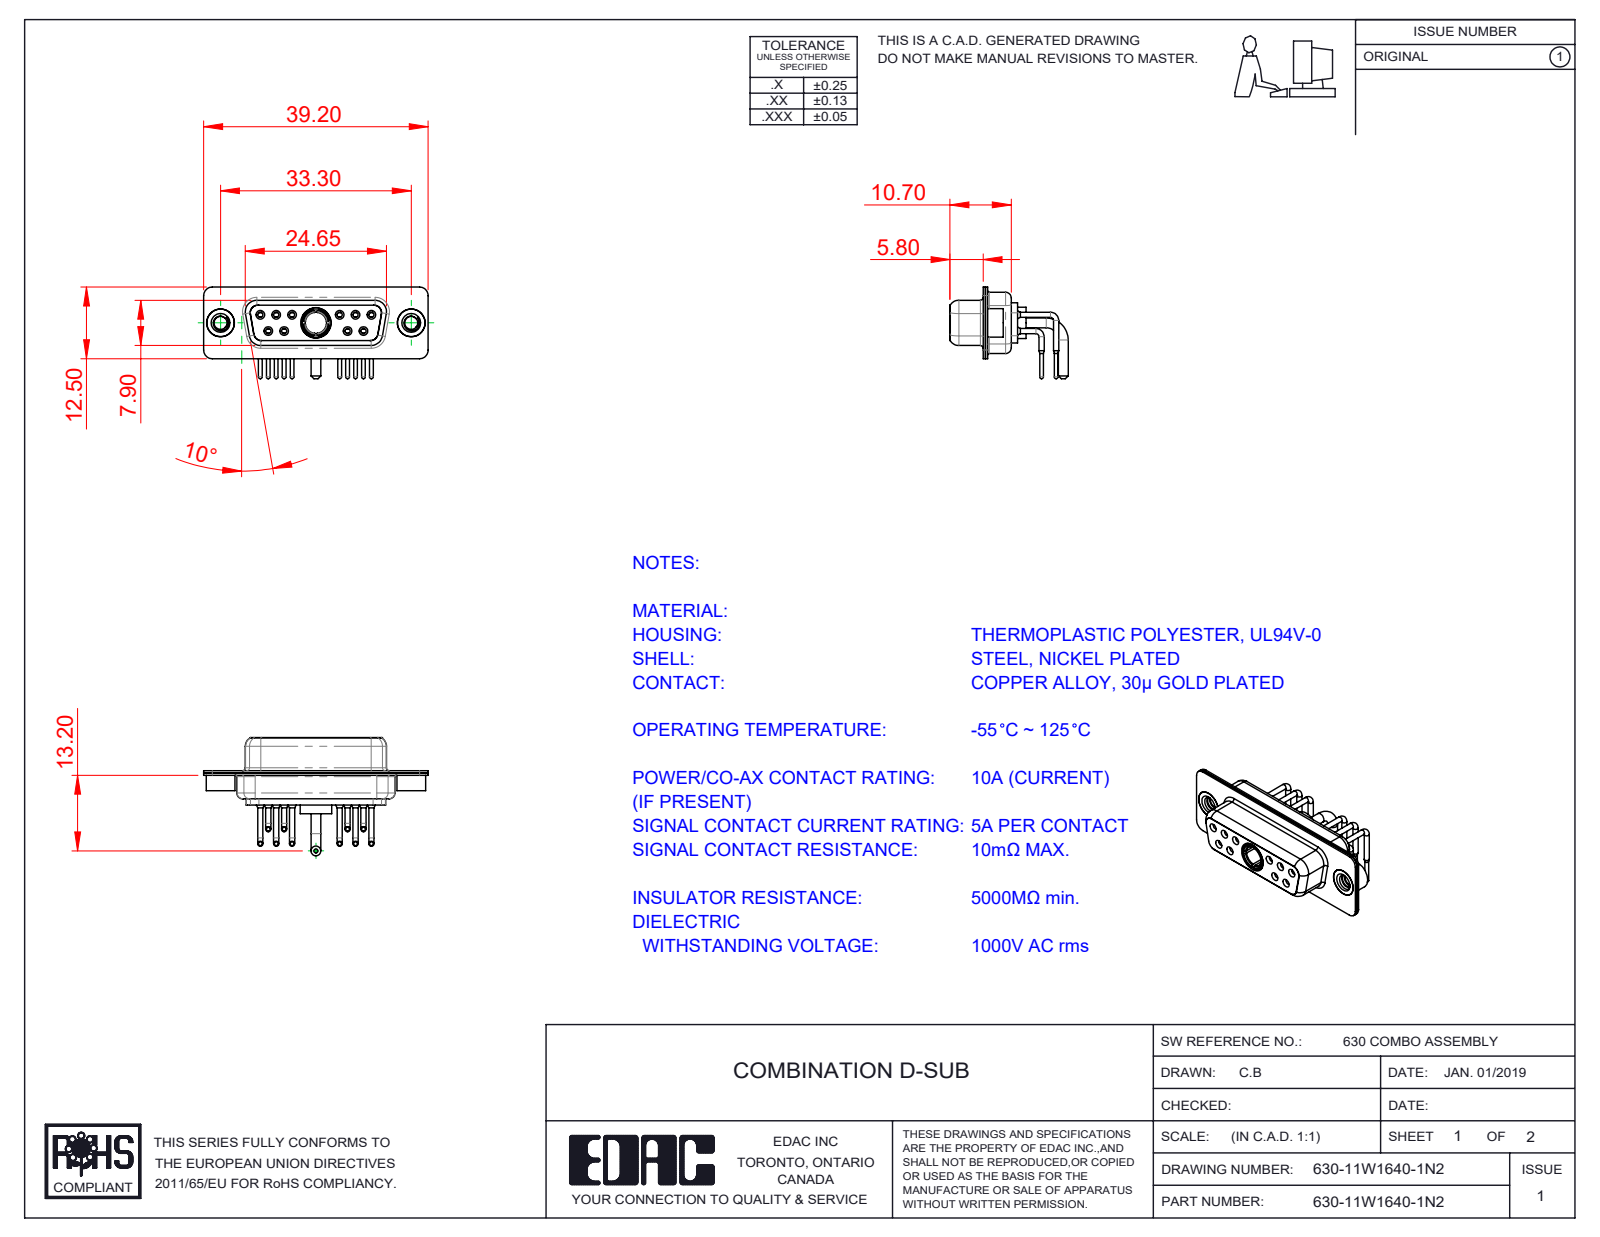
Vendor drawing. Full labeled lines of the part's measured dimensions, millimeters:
Part name (STEP PRODUCT): 630Combo Housing_11W1; 630-11W1640-1N2; Power Socket_10A RA; 630Combo Contact Row 1 (+4 more)
STEP written by: SolidWorks 2020 (CONFIG_CONTROL_DESIGN)
Units: millimetres
Bodies: 17 solids, 887 faces (246 planar, 392 cylindrical, 249 other)
Overall size (bounding box): 39.2 × 20.65 × 16
Volume: 2 589 mm³ · Surface area: 6 221 mm²
Round holes (diameter × count): ⌀0.9 ×10, ⌀1.1 ×10, ⌀1.5 ×10, ⌀2 ×10, ⌀1.7 ×6, ⌀1.6 ×4, ⌀4.85 ×3, ⌀2.26 ×2, ⌀4 ×2, ⌀4.05 ×2, ⌀3.7 ×1, ⌀5.3 ×1
Round bosses / shafts (diameter × count): ⌀0.9 ×10, ⌀0.65 ×10, ⌀1.6 ×6, ⌀5 ×2, ⌀4.95 ×2, ⌀4.8 ×2, ⌀1.7 ×2, ⌀5.5 ×1
Partial cylindrical surfaces — rounded edges, fillets, slot ends (radius × count): R1.5 ×16, R1.35 ×12, R2 ×12, R1.6 ×8, R0.25 ×4, R0.5 ×4, R0.6 ×4, R0.65 ×4
Main face-to-face distances: 0.4, 1.4, 0.45, 8.45, 1.8, 8.9, 0.8, 6.2, 7.05, 1.85
Hole centre spacings: 3.16, 2.77, 13.85, 11.08, 16.62, 5.03, 5.04, 5.54
